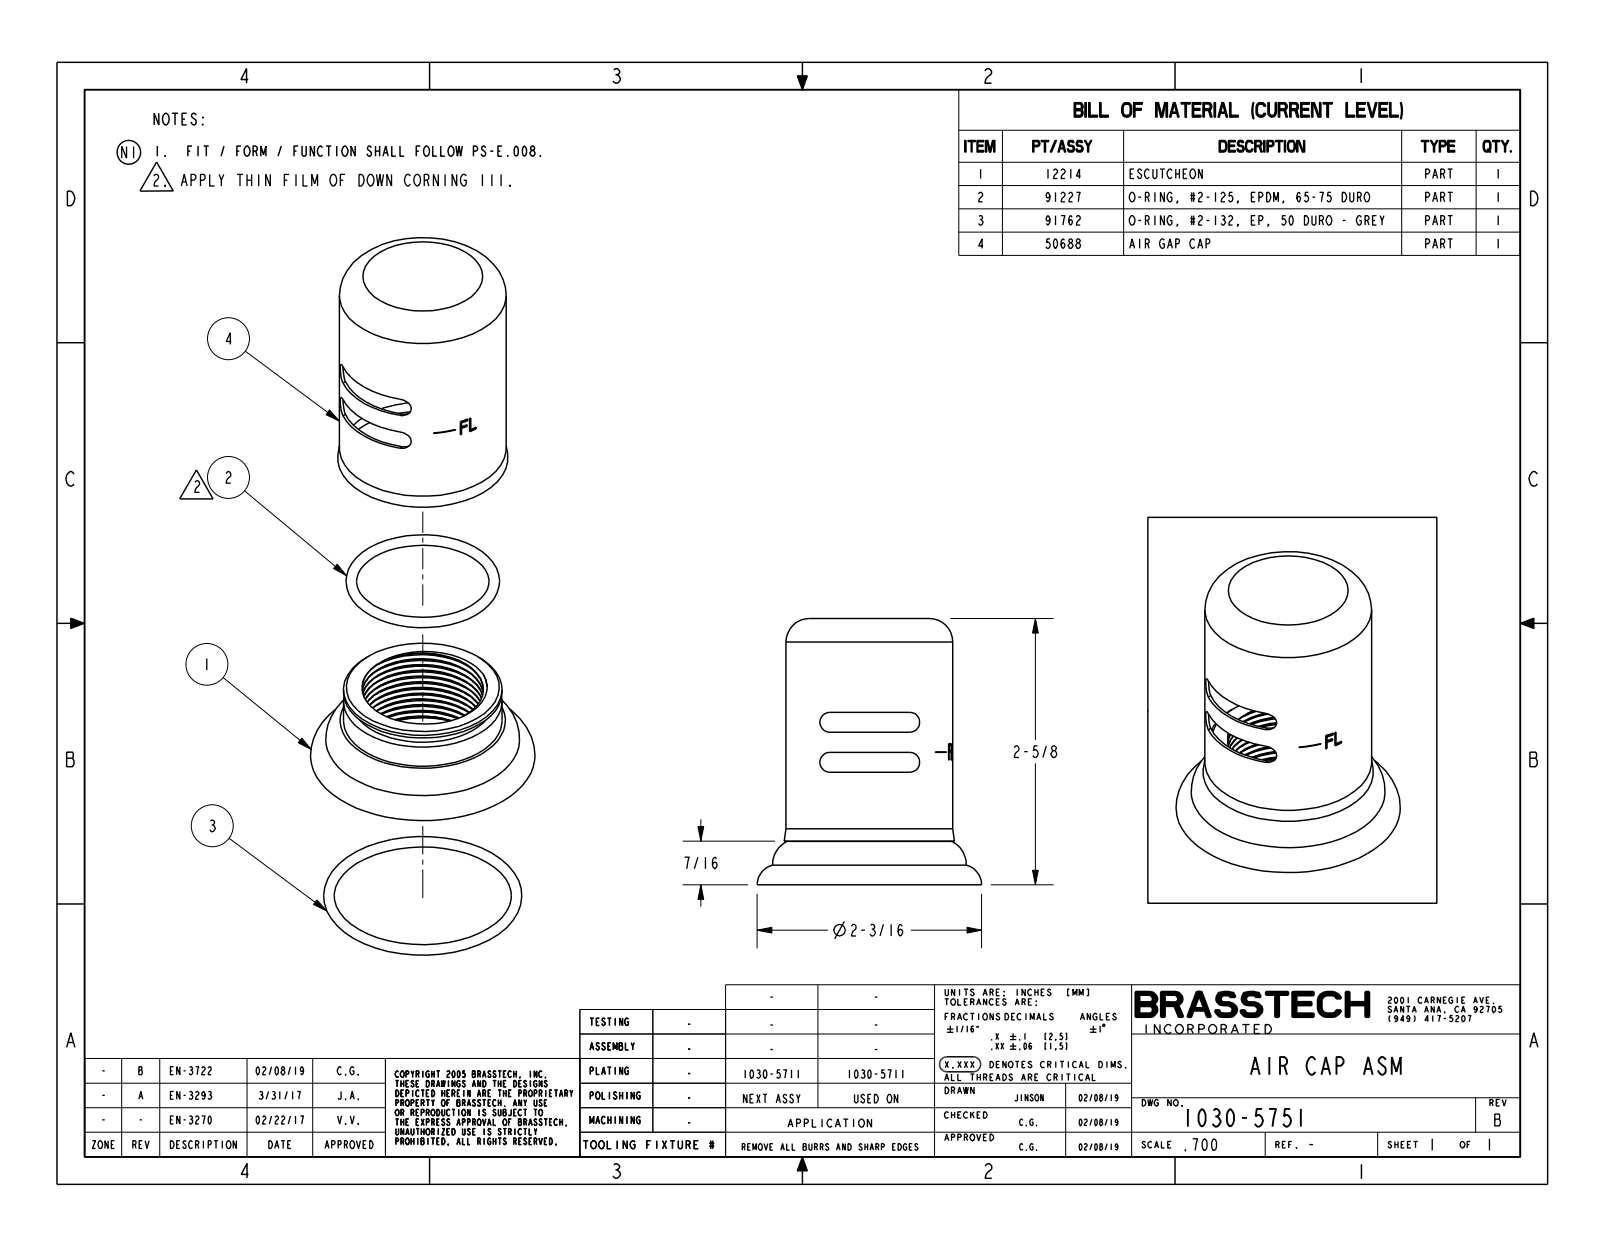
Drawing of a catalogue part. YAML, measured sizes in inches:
part_name: "12214; 91227; 91394; 50688 (+1 more)"
step_written_by: "PRO/ENGINEER BY PARAMETRIC TECHNOLOGY CORPORATION, 2013150 (CONFIG_CONTROL_DESIGN)"
units: inches
bodies: {solids: 4, faces: 137, planar: 37, cylindrical: 52, other: 48}
overall_size: [2.699, 2.2, 2.2]
volume: 1.843
surface_area: 68.91
round_holes:
  - {diameter: 1.19, count: 1}
  - {diameter: 1.57, count: 1}
  - {diameter: 1.99, count: 1}
round_bosses_or_shafts:
  - {diameter: 1.75, count: 1}
  - {diameter: 1.696, count: 1}
  - {diameter: 1.558, count: 1}
  - {diameter: 1.39, count: 1}
partial_cylinders:
  - {radius: 0.094, count: 4}
  - {radius: 0.805, count: 1}
face_to_face_distances: [2.676, 0.825, 1.851, 2.613, 1.788, 0.063, 0.655, 0.17, 1.958, 2.021]
